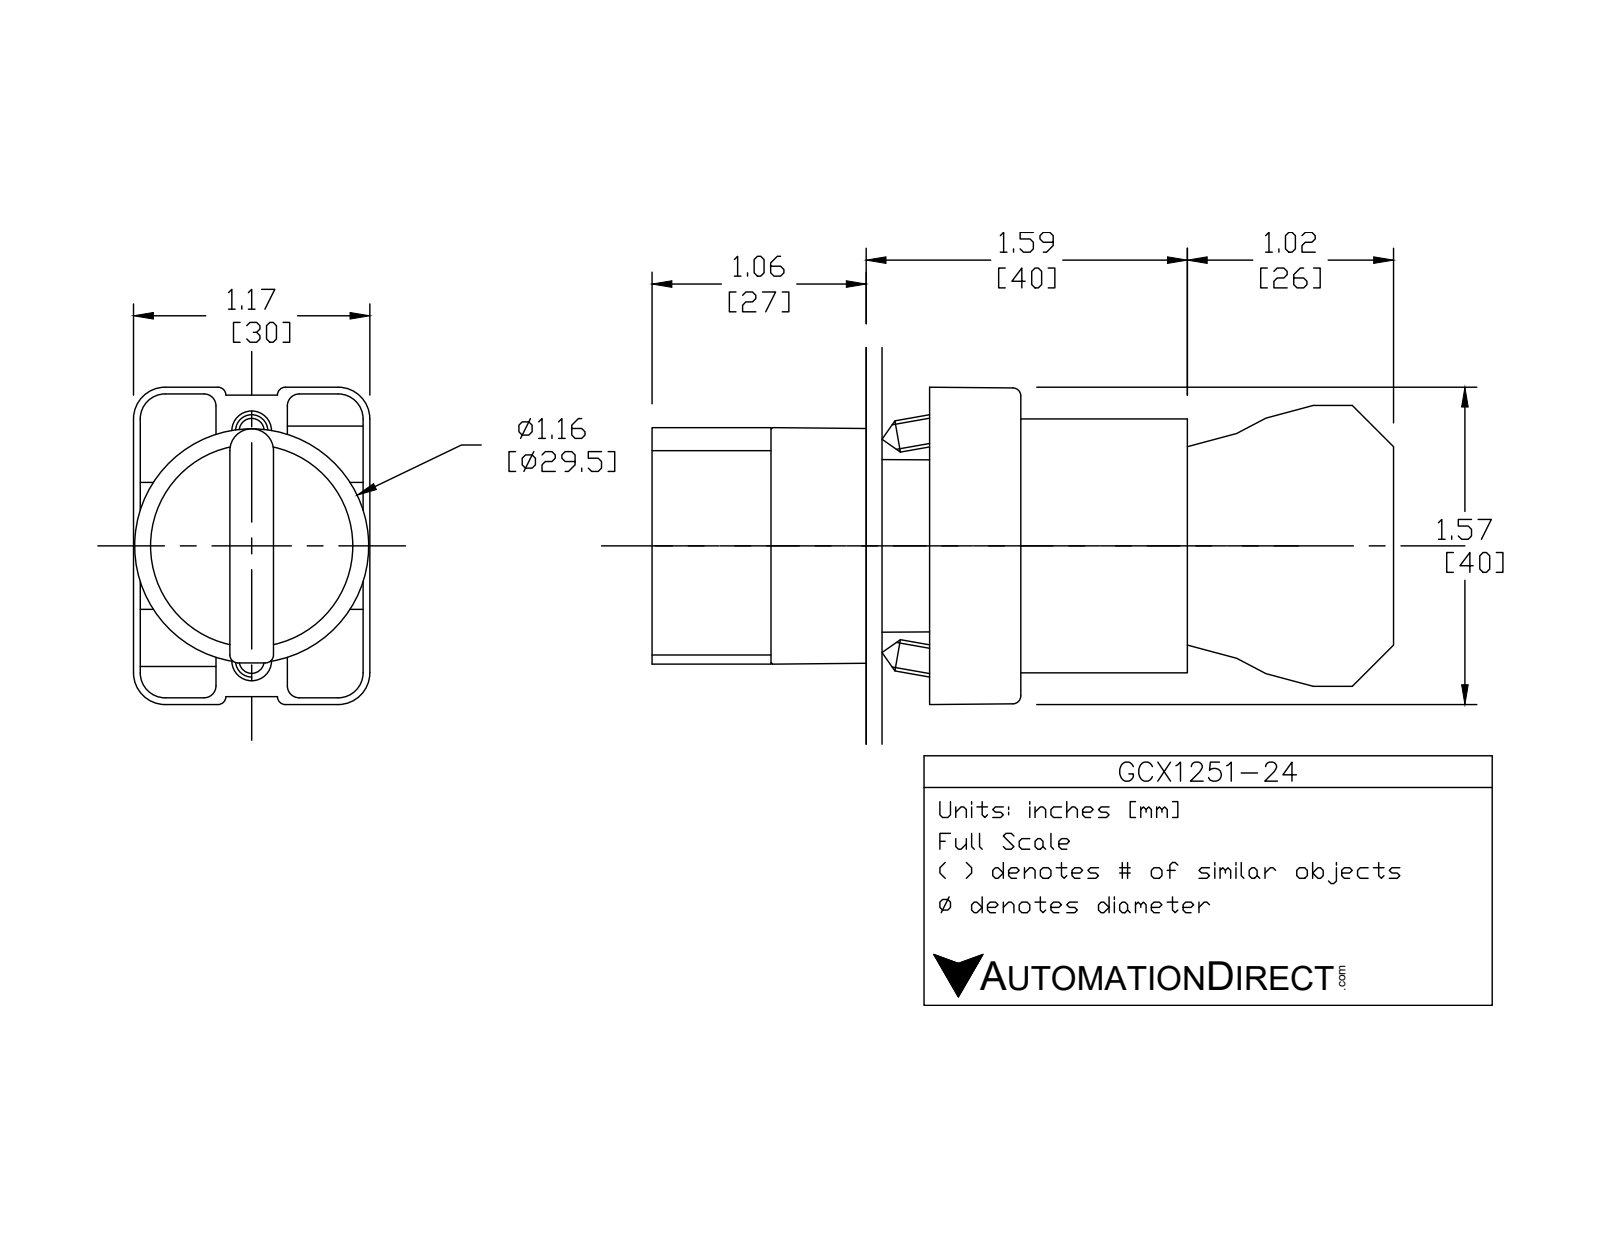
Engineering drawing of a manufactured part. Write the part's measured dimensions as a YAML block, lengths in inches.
part_name: "GCX1251-24; ECX1050; ecx1029; ecx1040 (+1 more)"
step_written_by: "SolidWorks 2016 (AUTOMOTIVE_DESIGN)"
units: inches
bodies: {solids: 8, faces: 445, planar: 263, cylindrical: 151, other: 31}
overall_size: [3.653, 1.581, 1.177]
volume: 2.799
surface_area: 39
round_holes:
  - {diameter: 0.079, count: 2}
  - {diameter: 0.124, count: 2}
  - {diameter: 0.13, count: 2}
  - {diameter: 0.087, count: 1}
  - {diameter: 0.197, count: 1}
  - {diameter: 0.469, count: 1}
  - {diameter: 0.878, count: 1}
  - {diameter: 0.888, count: 1}
  - {diameter: 1.024, count: 1}
round_bosses_or_shafts:
  - {diameter: 0.157, count: 4}
  - {diameter: 1.175, count: 1}
  - {diameter: 1.004, count: 1}
  - {diameter: 0.945, count: 1}
  - {diameter: 0.856, count: 1}
  - {diameter: 0.78, count: 1}
  - {diameter: 0.504, count: 1}
partial_cylinders:
  - {radius: 0.059, count: 24}
  - {radius: 0.041, count: 12}
  - {radius: 0.124, count: 12}
  - {radius: 0.157, count: 12}
  - {radius: 0.039, count: 9}
  - {radius: 0.128, count: 2}
  - {radius: 0.02, count: 1}
  - {radius: 0.063, count: 1}
face_to_face_distances: [0.827, 2.02, 1.193, 0.579, 1.244, 1.171, 0.472, 0.469, 0.031, 0.033]
hole_center_spacings: [0.236, 0.544, 0.472, 0.49]
